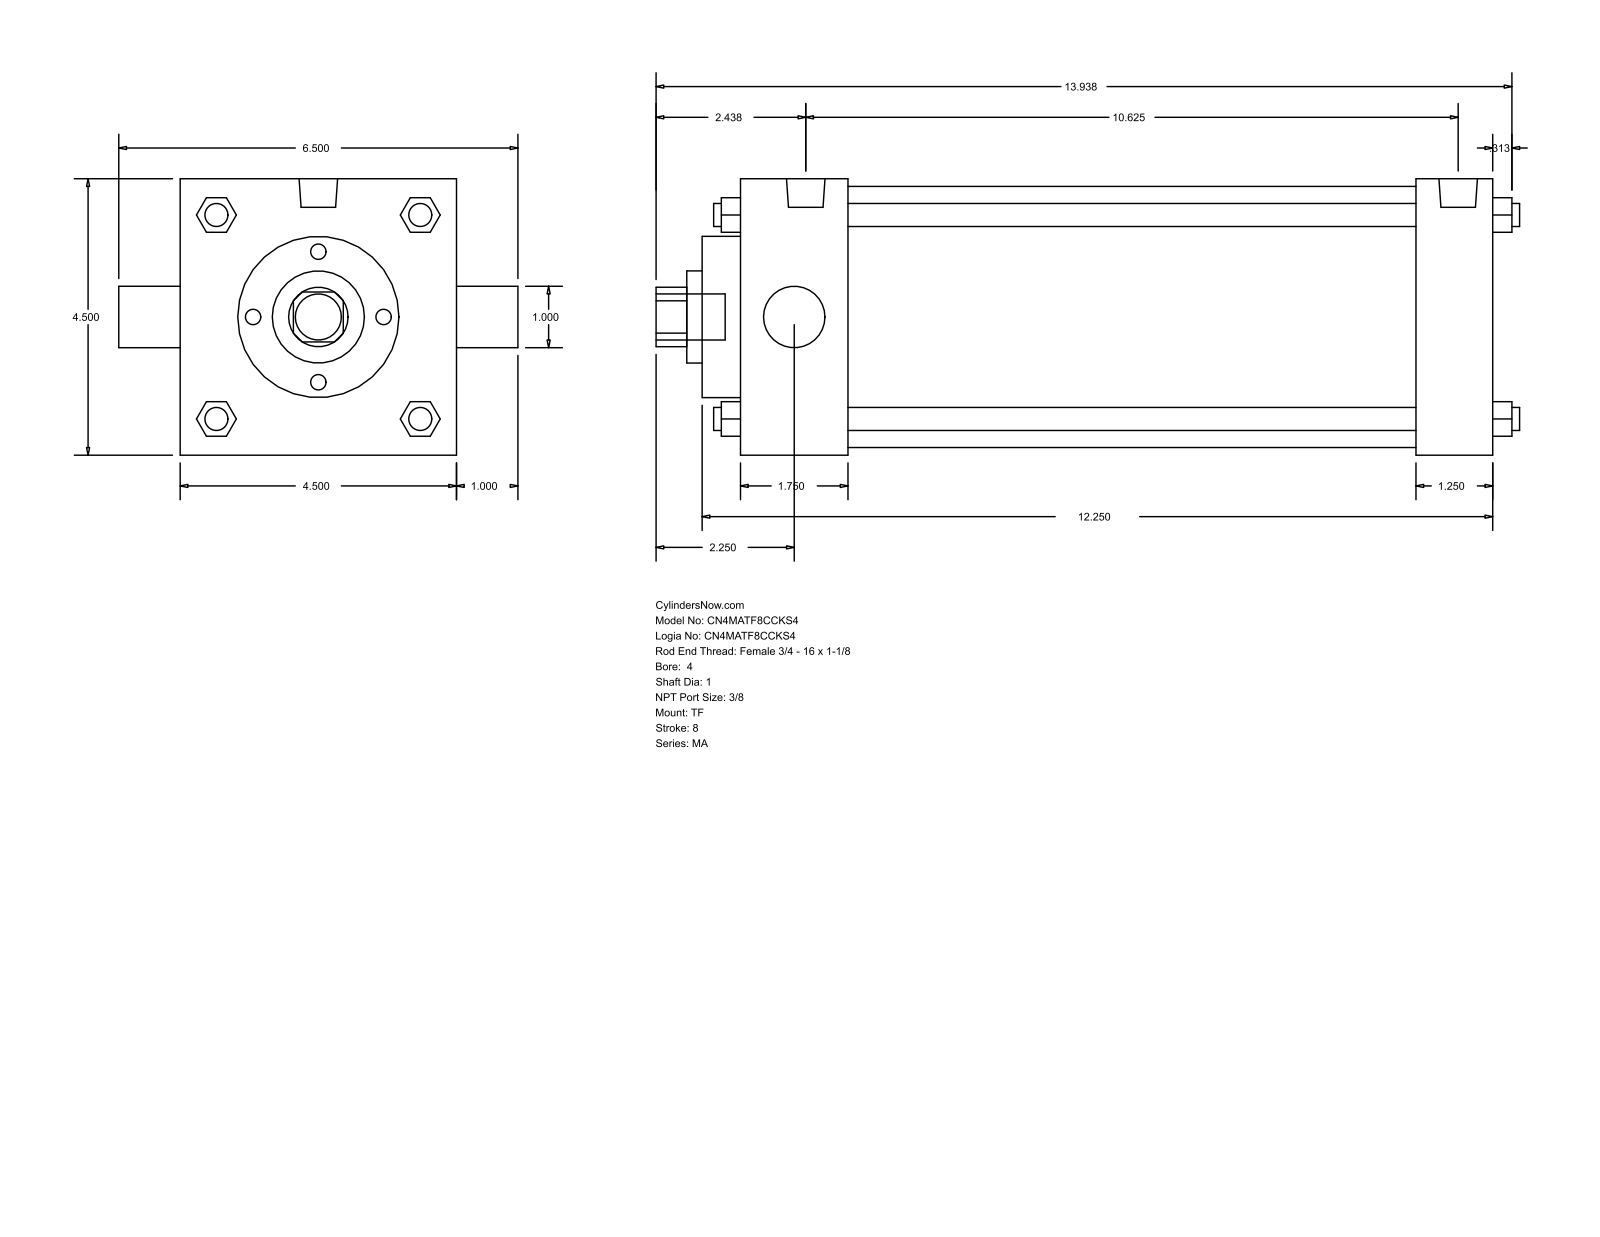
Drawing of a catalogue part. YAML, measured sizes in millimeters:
part_name: "MA_TF__0400_1"
step_written_by: "GSSL Pune (CONFIG_CONTROL_DESIGN)"
units: millimeters
bodies: {solids: 0, faces: 122, planar: 93, cylindrical: 29, other: 0}
overall_size: [357.19, 165.1, 114.3]
round_holes:
  - {diameter: 25.4, count: 2}
  - {diameter: 38.1, count: 1}
  - {diameter: 66.67, count: 1}
  - {diameter: 107.95, count: 1}
round_bosses_or_shafts:
  - {diameter: 9.53, count: 4}
  - {diameter: 11.11, count: 3}
  - {diameter: 15.93, count: 2}
  - {diameter: 19.05, count: 1}
partial_cylinders:
  - {radius: 12.29, count: 1}
face_to_face_distances: [114.3, 311.15, 279.4, 31.75, 44.46, 234.94, 266.69, 327.02, 15.87, 60.33]
